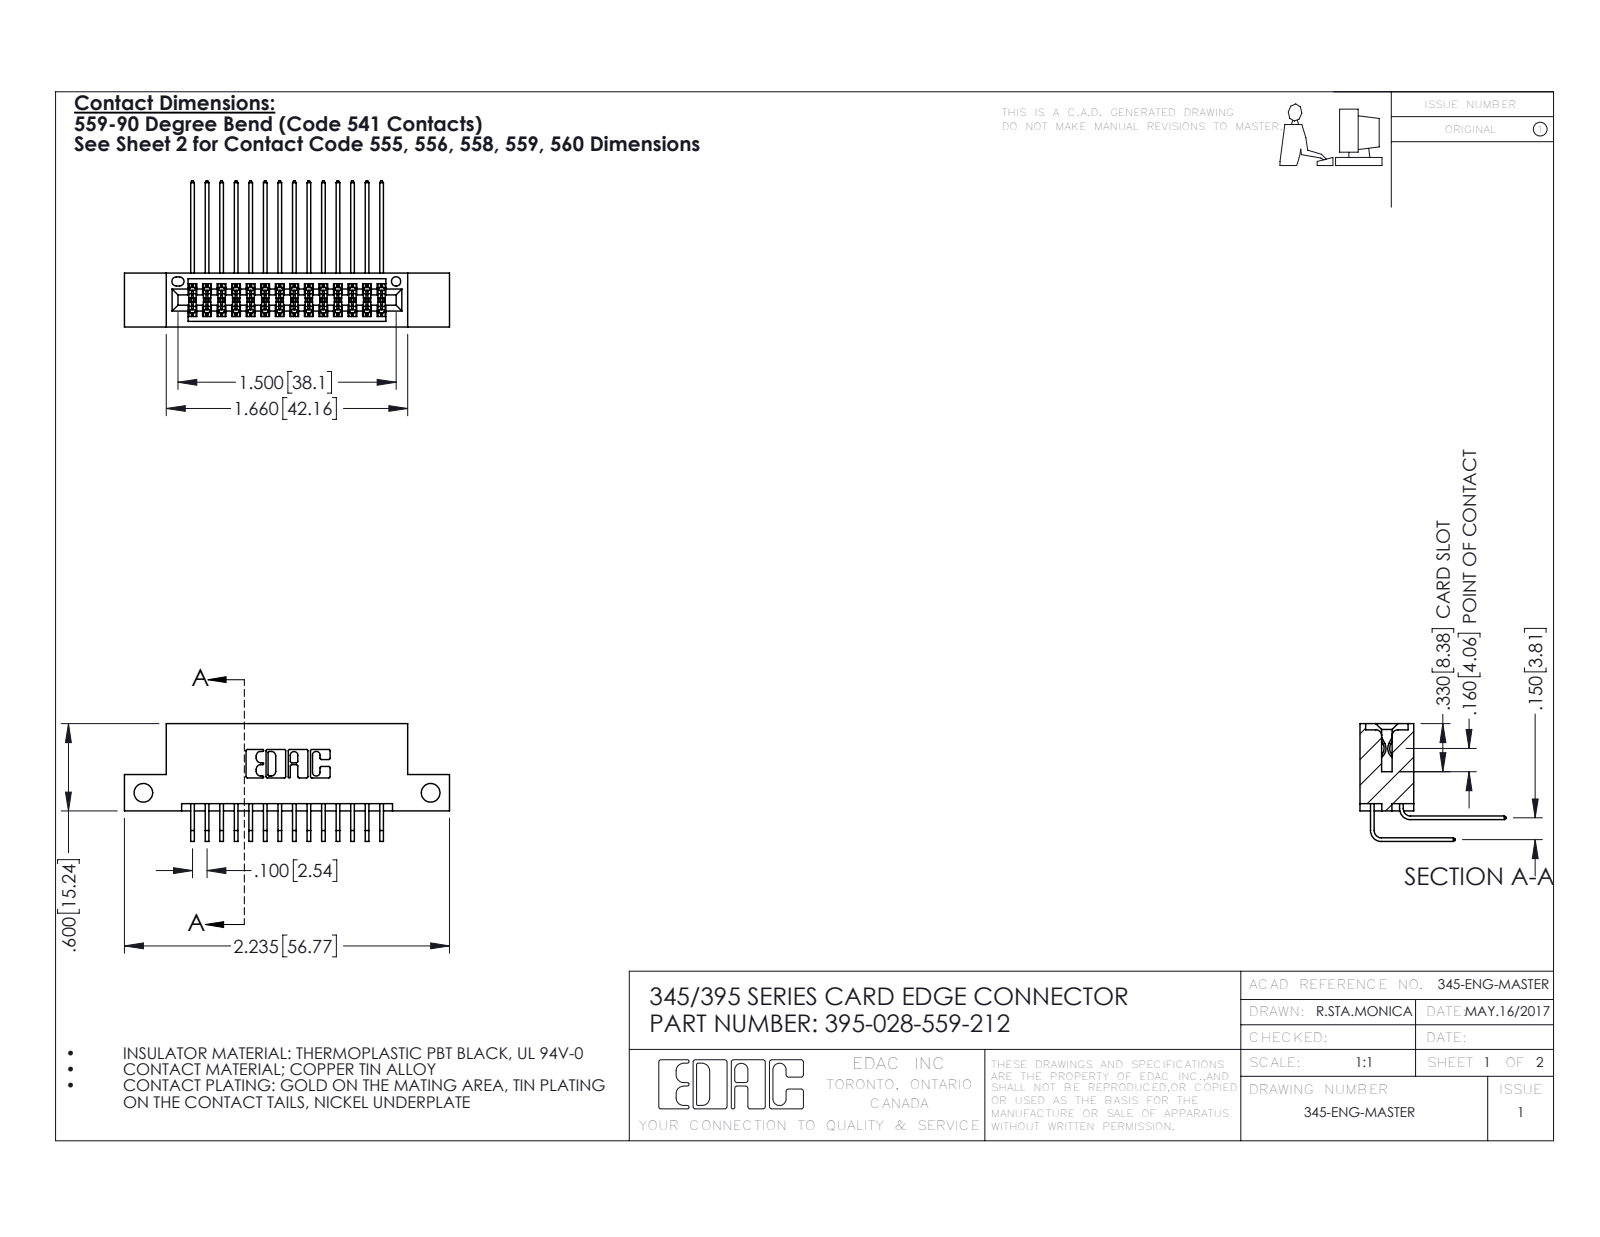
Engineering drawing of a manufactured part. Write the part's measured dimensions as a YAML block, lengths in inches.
part_name: "345-292-001_559 Tail - 2; 345-292-001_558 559 Tail - 1; 395-028-559-212; 345 Part_Flush Mounting Lugs - Side Mount"
step_written_by: "SolidWorks 2016 (CONFIG_CONTROL_DESIGN)"
units: inches
bodies: {solids: 29, faces: 1582, planar: 1060, cylindrical: 522, other: 0}
overall_size: [2.235, 1.005, 0.809]
volume: 0.325
surface_area: 12.34
round_holes:
  - {diameter: 0.128, count: 2}
  - {diameter: 0.064, count: 1}
partial_cylinders:
  - {radius: 0.006, count: 42}
  - {radius: 0.01, count: 22}
  - {radius: 0.007, count: 6}
  - {radius: 0.031, count: 6}
  - {radius: 0.026, count: 3}
  - {radius: 0.014, count: 2}
  - {radius: 0.019, count: 2}
  - {radius: 0.022, count: 2}
face_to_face_distances: [0.2, 0.072, 0.298, 0.37, 0.098, 0.272, 0.025, 0.225, 0.15, 0.175]
hole_center_spacings: [1.975]
